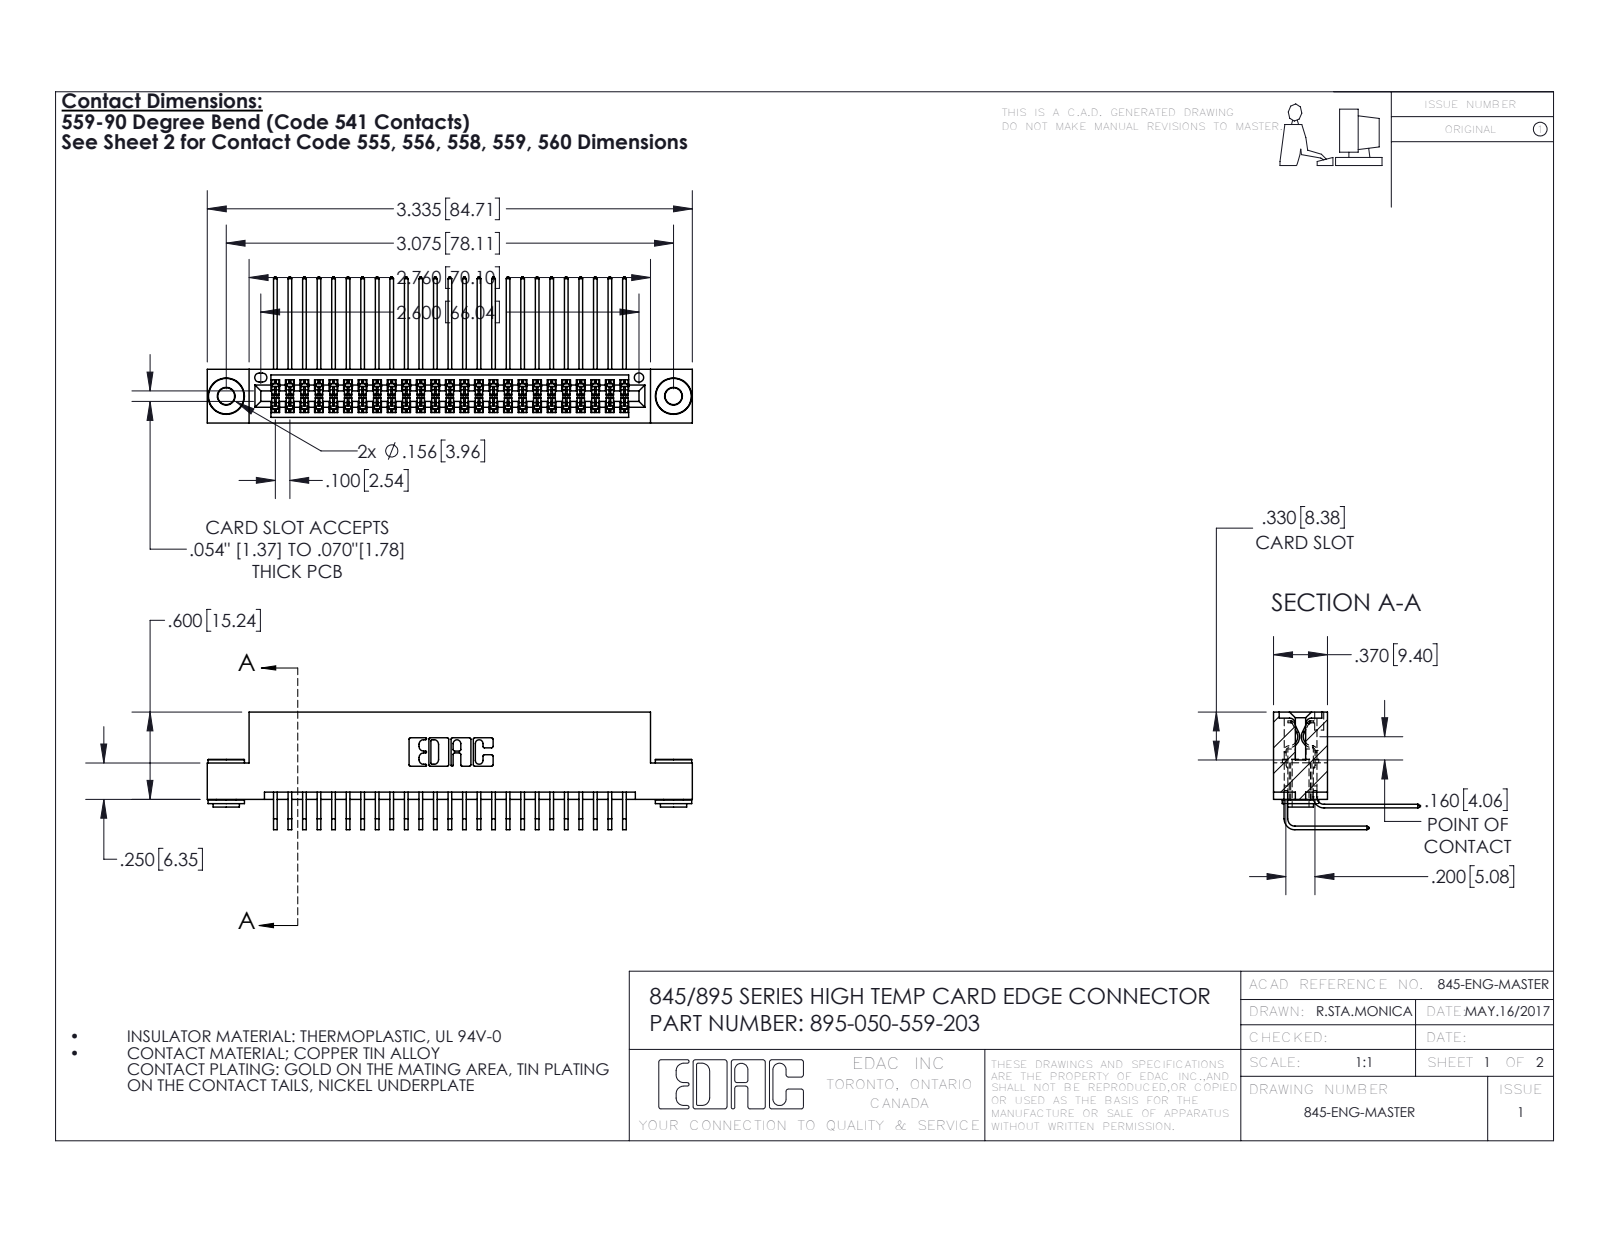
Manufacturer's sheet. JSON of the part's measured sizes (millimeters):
{"part_name": "345-292-001_558 559 Tail - 1; 345-250-002_345-250-002-102; 345-292-001_559 Tail - 2; 395-050-559-203 (+1 more)", "step_written_by": "SolidWorks 2016 (CONFIG_CONTROL_DESIGN)", "units": "millimeters", "bodies": {"solids": 53, "faces": 2764, "planar": 1840, "cylindrical": 916, "other": 8}, "overall_size": [84.7, 25.5, 20.5], "volume_mm3": 8370, "surface_area_mm2": 13620, "round_holes": [[2.9, 2], [4, 2], [1.6, 1]], "round_bosses_or_shafts": [[6.4, 2], [4.6, 2], [3.5, 2]], "partial_cylinders_radius": [[0.2, 100], [0.3, 22], [0.2, 6], [0.8, 6], [0.7, 3], [0.4, 2], [0.5, 2], [0.6, 2]], "face_to_face_distances": [1.8, 7.6, 5.1, 9.4, 0.6, 2.5, 6.9, 5.7, 3.8, 4.4], "hole_center_spacings": [6.9, 72.1, 78.1]}
